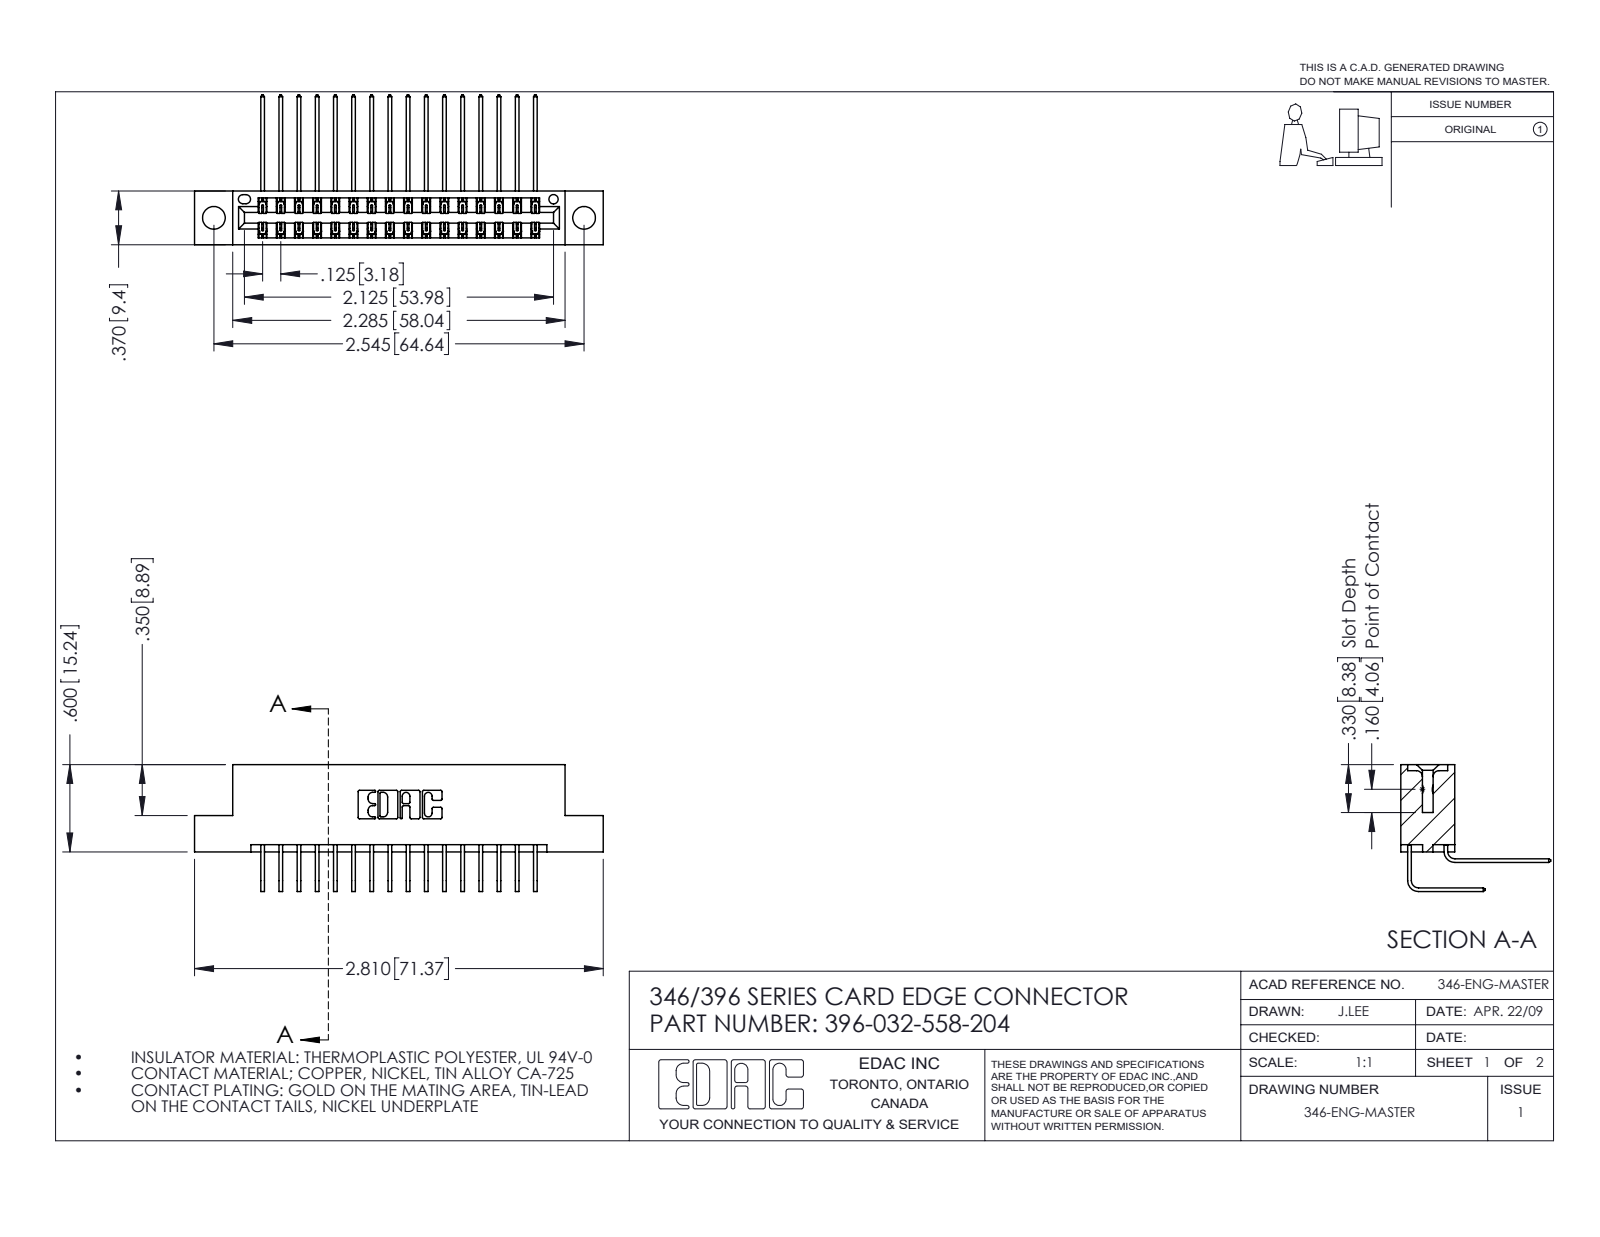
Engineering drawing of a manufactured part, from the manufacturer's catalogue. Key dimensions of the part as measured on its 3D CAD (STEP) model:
Part name (STEP PRODUCT): 345-292-001_558 Tail - 2; 345-292-001_558 559 Tail - 1; 396-032-558-204; 346 Part_Flush Mounting Lugs - 0.156 Dia-TH
STEP written by: SolidWorks 2016 (CONFIG_CONTROL_DESIGN)
Units: inches
Bodies: 33 solids, 1850 faces (1260 planar, 590 cylindrical, 0 other)
Overall size (bounding box): 2.81 × 1.03 × 0.873
Volume: 0.418 in³ · Surface area: 15.05 in²
Round holes (diameter × count): ⌀0.156 ×2, ⌀0.064 ×1
Partial cylindrical surfaces — rounded edges, fillets, slot ends (radius × count): R0.006 ×48, R0.01 ×22, R0.007 ×6, R0.031 ×6, R0.026 ×3, R0.014 ×2, R0.022 ×2, R0.024 ×2
Main face-to-face distances: 0.322, 0.048, 0.25, 0.025, 0.37, 0.298, 0.072, 0.275, 0.148, 0.222
Hole centre spacings: 0.246, 2.338, 2.545
